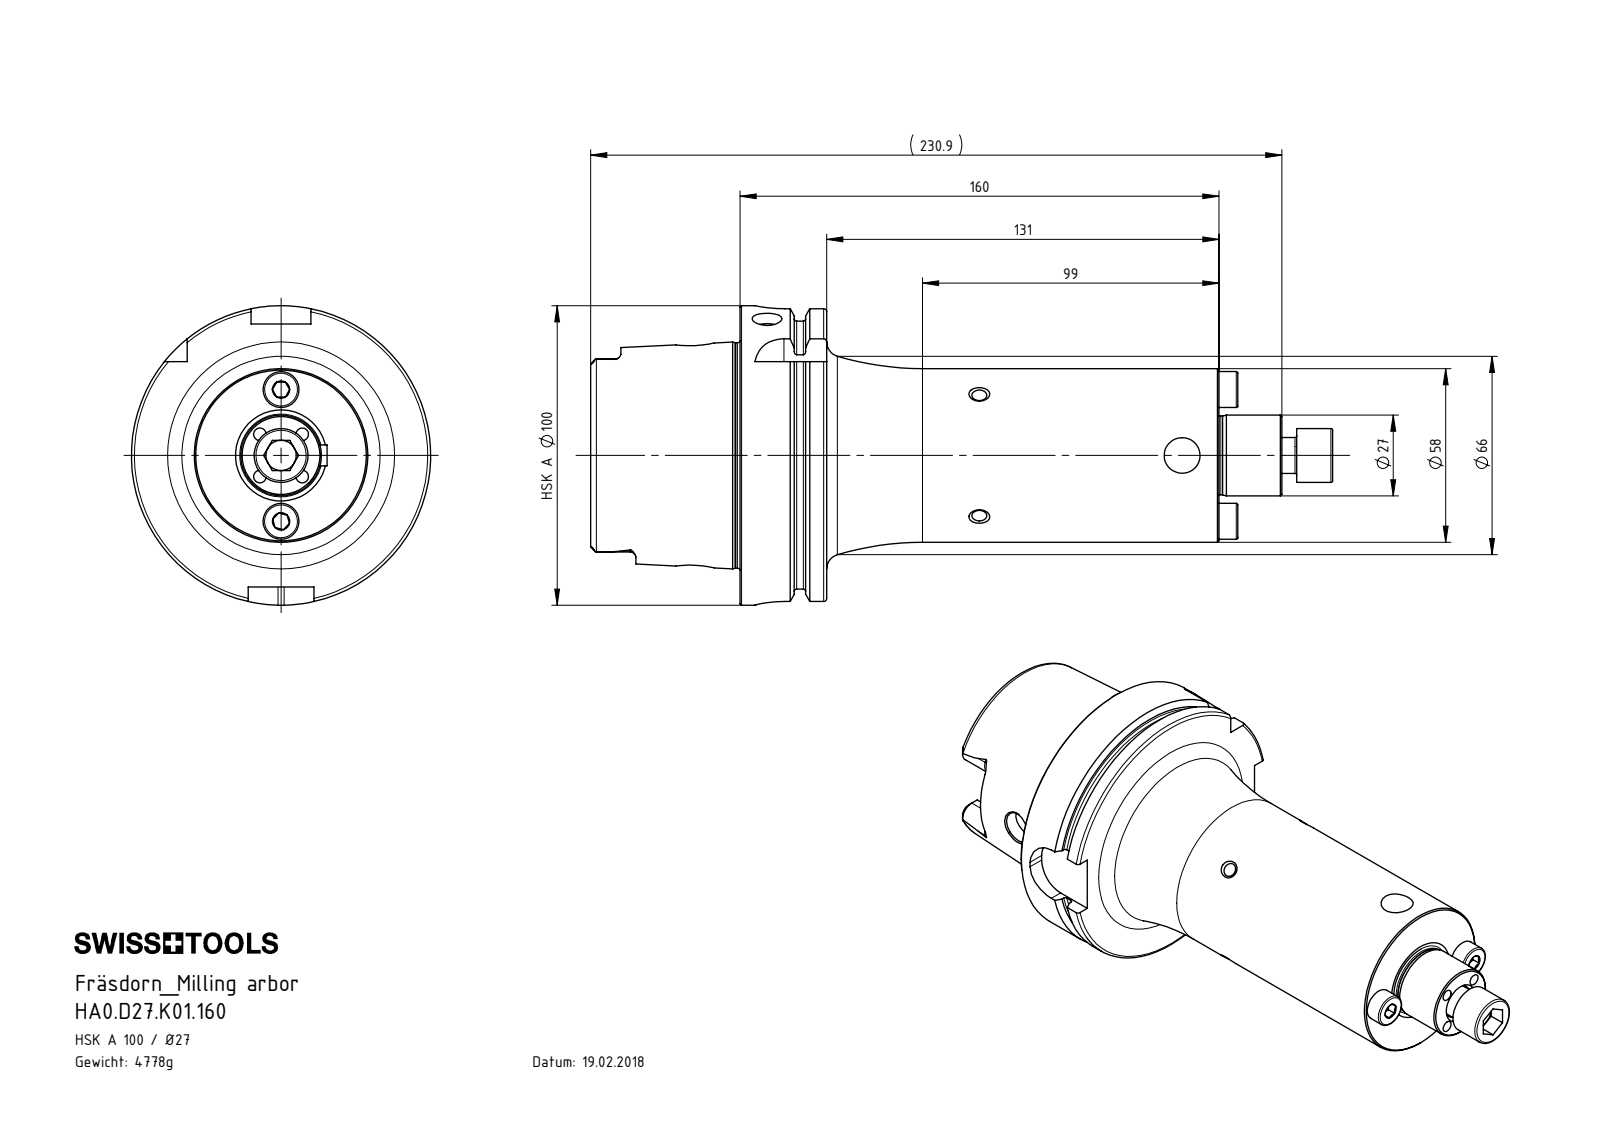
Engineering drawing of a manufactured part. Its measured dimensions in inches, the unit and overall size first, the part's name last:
Units: inches
Overall size (bounding box): 9.76 × 3.937 × 3.937
Round holes (diameter × count): ⌀0.165 ×6, ⌀0.197 ×6, ⌀0.394 ×5, ⌀0.472 ×2, ⌀0.402 ×1, ⌀0.512 ×1, ⌀0.886 ×1, ⌀1.024 ×1, ⌀2.087 ×1, ⌀2.48 ×1
Round bosses / shafts (diameter × count): ⌀0.472 ×2, ⌀0.236 ×2, ⌀0.181 ×2, ⌀3.937 ×1, ⌀3.62 ×1, ⌀2.963 ×1, ⌀2.283 ×1, ⌀1.063 ×1
Partial cylindrical surfaces — rounded edges, fillets, slot ends (radius × count): R0.075 ×6, R0.192 ×4, R0.394 ×4, R0.138 ×2, R0.157 ×2
Main face-to-face distances: 1.14, 6.299, 5.159, 0.49, 0.65, 5.809, 1.965, 2.455, 3.104, 8.264
Hole centre spacings: 0.394, 0.557, 0.65, 1.178, 2.758, 0.787, 0.866, 1.732
Volume: 37.14 in³ · Surface area: 137.9 in²
Bodies: 5 solids, 369 faces (89 planar, 118 cylindrical, 162 other)
Part name (STEP PRODUCT): HA0-D27.K01.160_D_Fertigbearbeitung; HA0.D27.K01.160; D27-ER3.001.016_A; D27-ER1.002.030_A (+1 more)
STEP written by: SolidWorks 2017 (AUTOMOTIVE_DESIGN)
